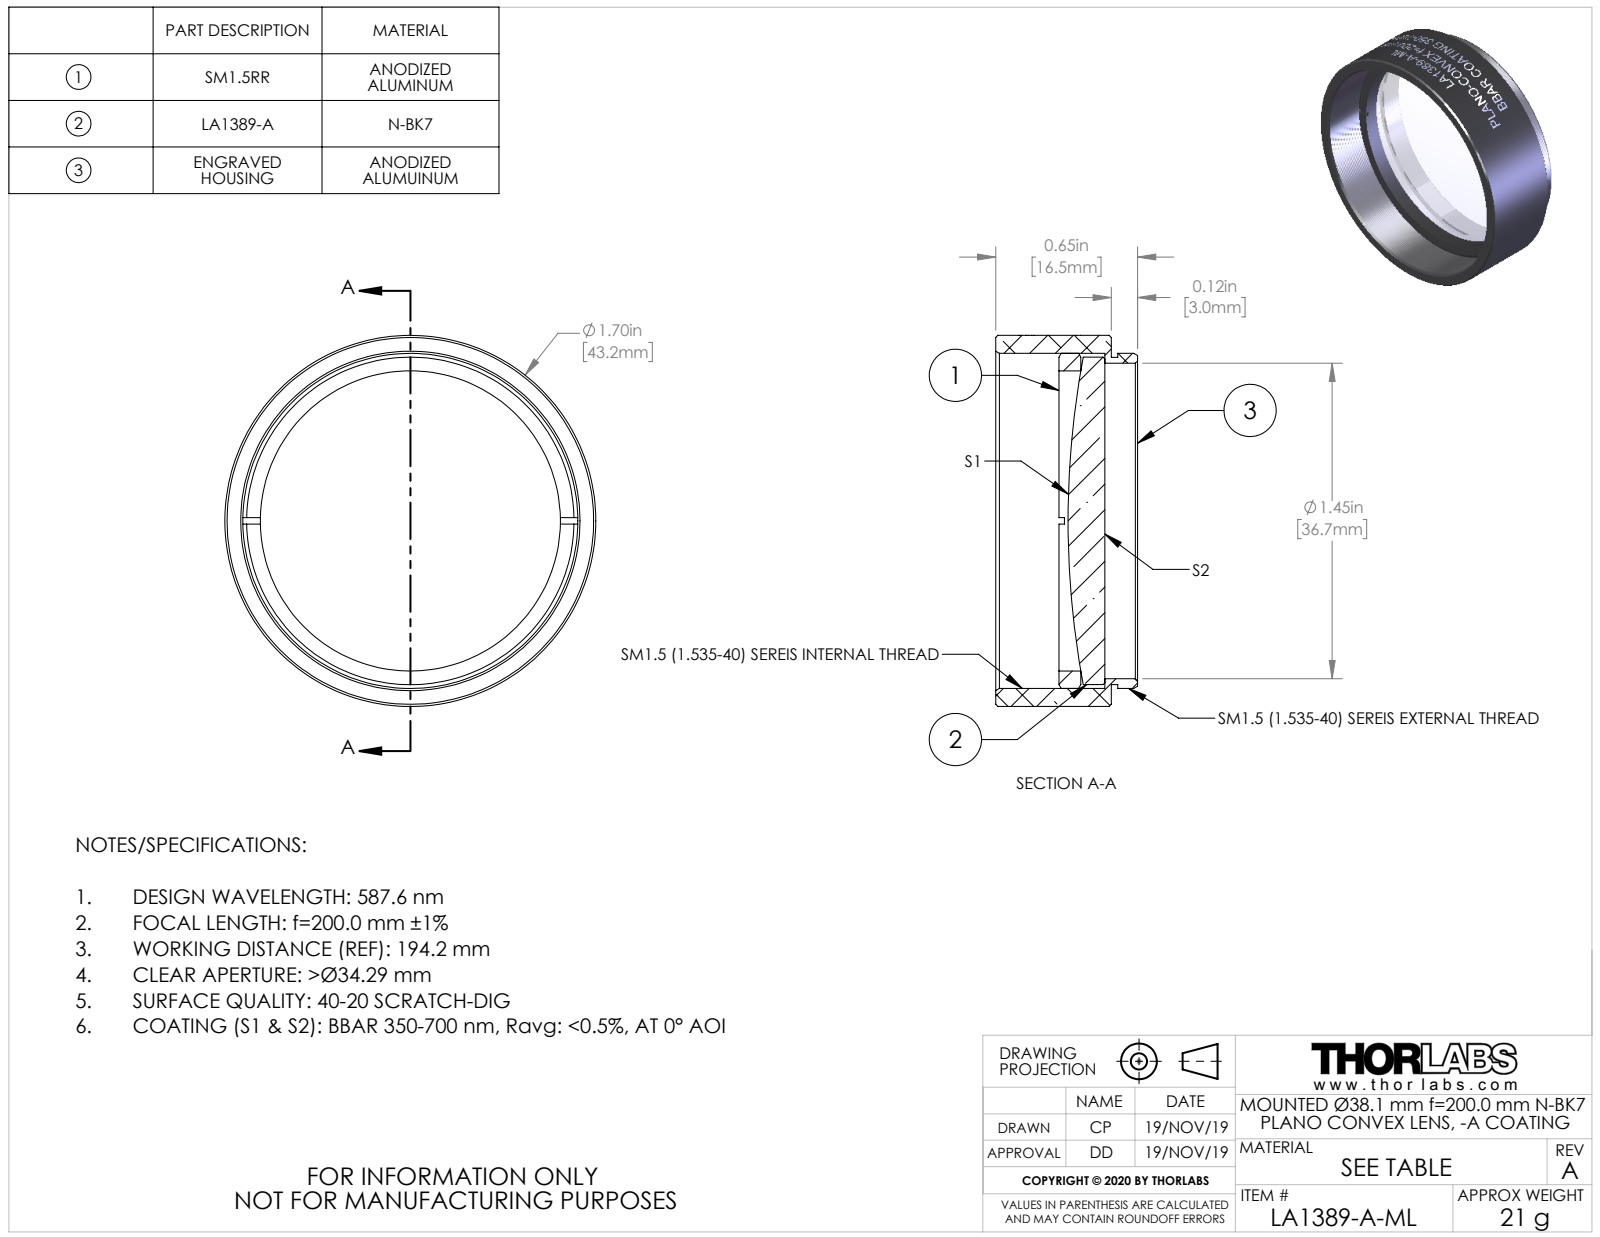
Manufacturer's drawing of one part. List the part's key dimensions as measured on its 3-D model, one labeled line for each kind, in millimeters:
Part name (STEP PRODUCT): TTN200724-E0W
STEP written by: SolidWorks 2018 (CONFIG_CONTROL_DESIGN)
Units: millimetres
Bodies: 3 solids, 159 faces (15 planar, 125 cylindrical, 19 other)
Overall size (bounding box): 43.18 × 43.18 × 16.51
Volume: 8 533 mm³ · Surface area: 8 607 mm²
Round holes (diameter × count): ⌀34.92 ×1, ⌀36.7 ×1
Round bosses / shafts (diameter × count): ⌀43.18 ×1, ⌀38.99 ×1, ⌀38.1 ×1, ⌀38.07 ×1
Main face-to-face distances: 0.76, 13.46, 12.7, 3.55, 2.79, 9.91, 6.09, 5.33, 2.54, 7.37
